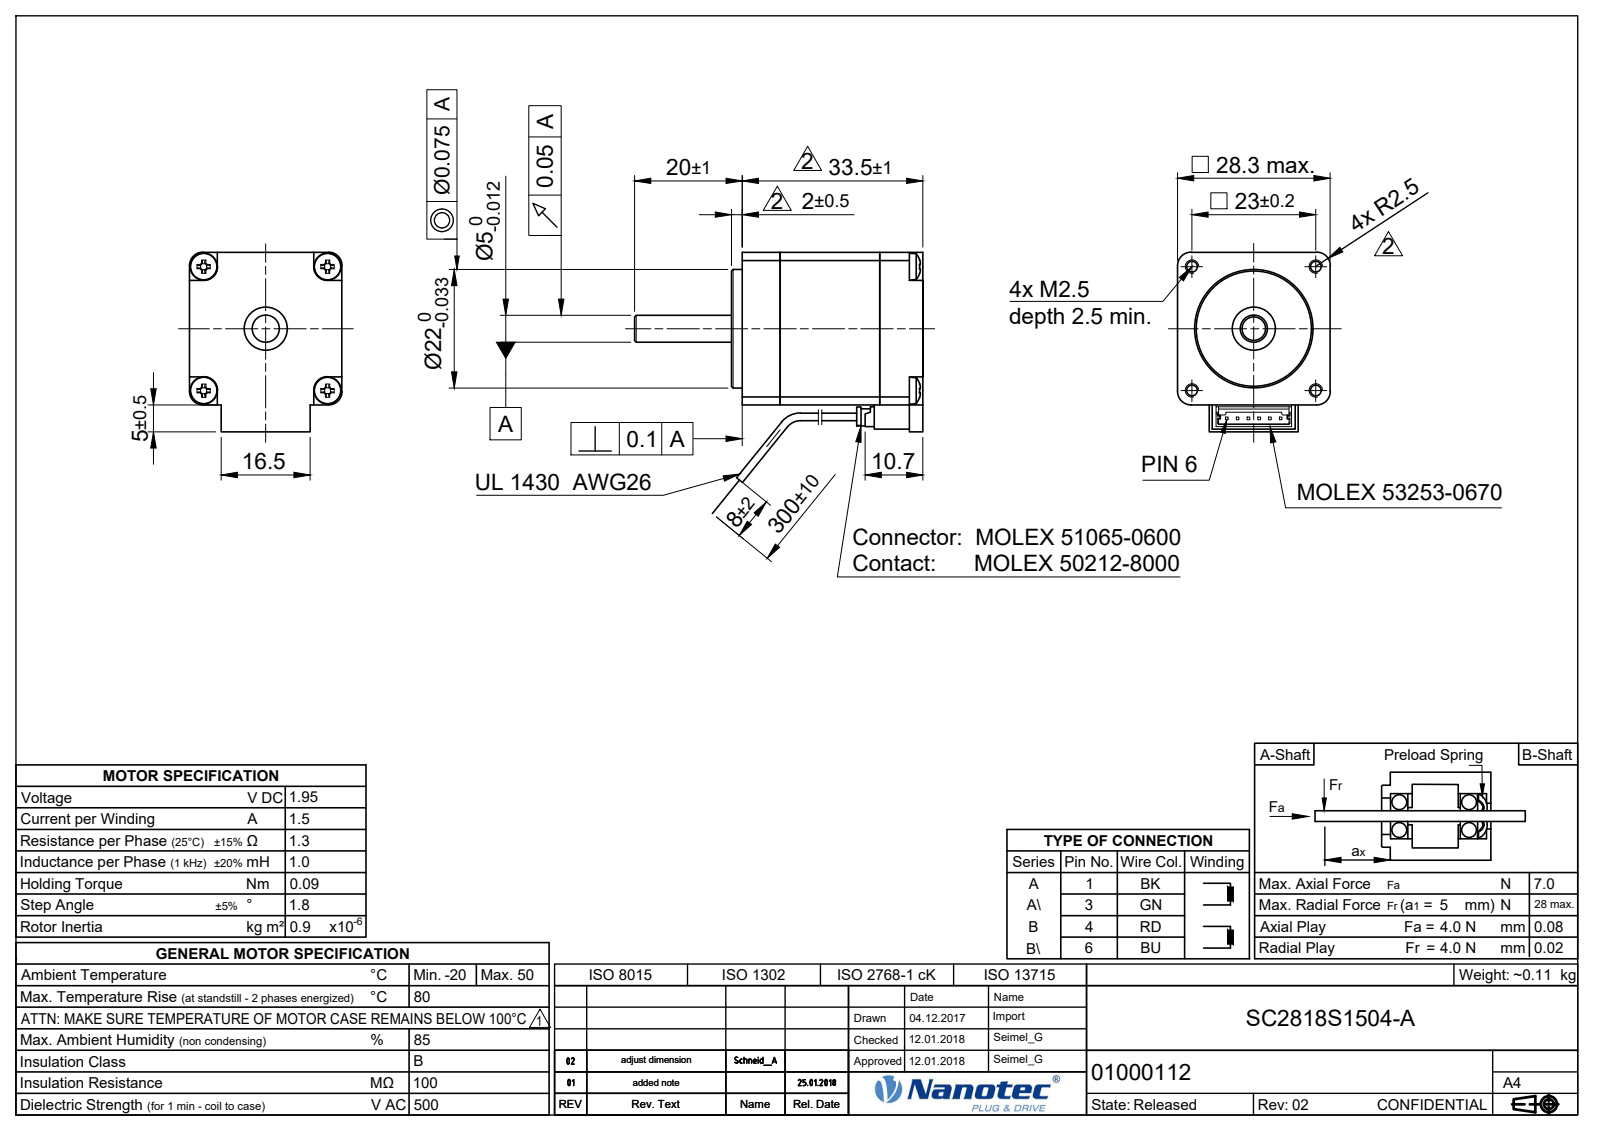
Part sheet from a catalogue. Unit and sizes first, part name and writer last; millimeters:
Units: millimetres
Overall size (bounding box): 53.5 × 33.3 × 28.3
Round holes (diameter × count): ⌀2.01 ×4, ⌀5 ×1, ⌀8 ×1
Round bosses / shafts (diameter × count): ⌀2.5 ×4, ⌀2.27 ×4, ⌀1.5 ×4, ⌀22 ×1
Partial cylindrical surfaces — rounded edges, fillets, slot ends (radius × count): R2.5 ×8, R0.2 ×3, R0.25 ×2, R0.5 ×2, R1 ×2
Main face-to-face distances: 28.3, 18.5, 8, 26.5, 25.5, 7, 33.5, 2, 0.5, 9
Hole centre spacings: 16.26, 23, 32.53
Volume: 28 167 mm³ · Surface area: 12 279 mm²
Bodies: 15 solids, 743 faces (599 planar, 56 cylindrical, 88 other)
Part name (STEP PRODUCT): SC2818Sxxx4-A
STEP written by: Autodesk Inventor 2021 (AUTOMOTIVE_DESIGN)
